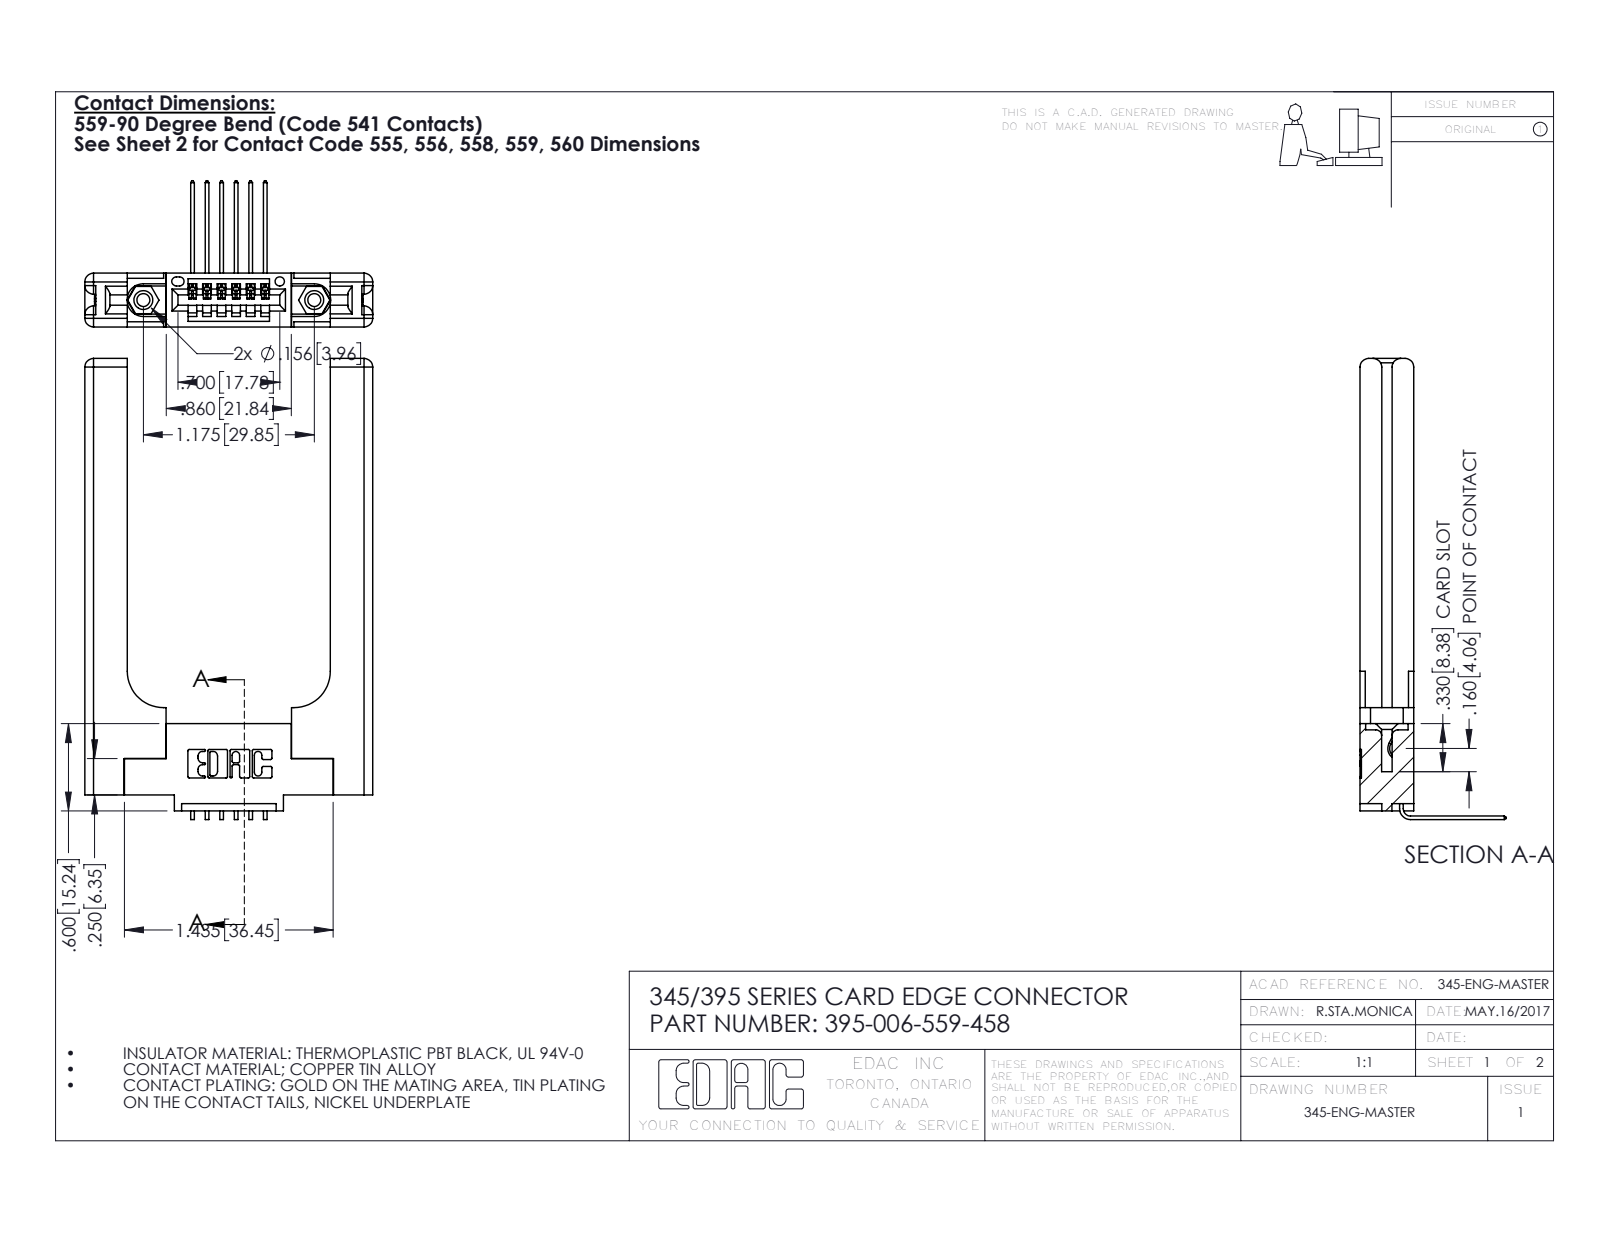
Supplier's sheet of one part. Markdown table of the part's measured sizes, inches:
| quantity | value |
| --- | --- |
| part name | 345-220-058_345-220-058; 345 Part_0.110 Offset - 0.156 Dia-TH; 395-006-559-458; 345-250-001_345-250-001-102 (+1 more) |
| STEP written by | SolidWorks 2016 (CONFIG_CONTROL_DESIGN) |
| units | inches |
| bodies | 11 solids, 746 faces (484 planar, 202 cylindrical, 60 other) |
| overall size | 3.169 × 1.979 × 1.005 |
| volume | 0.789 in³ |
| surface area | 16.89 in² |
| round holes (diameter × count) | 0.089 × 2, 0.125 × 2, 0.156 × 2, 0.064 × 1 |
| round bosses / shafts (diameter × count) | 0.155 × 2 |
| partial cylindrical surfaces (radius × count) | 0.01 × 22, 0.06 × 16, 0.006 × 12, 0.007 × 6, 0.031 × 6, 0.026 × 3, 0.03 × 2, 0.031 × 2 |
| main face-to-face distances | 0.37, 0.15, 0.22, 0.072, 1.396, 0.148, 0.077, 0.071, 0.298, 0.292 |
| hole center spacings | 0.27, 0.946, 1.175 |
